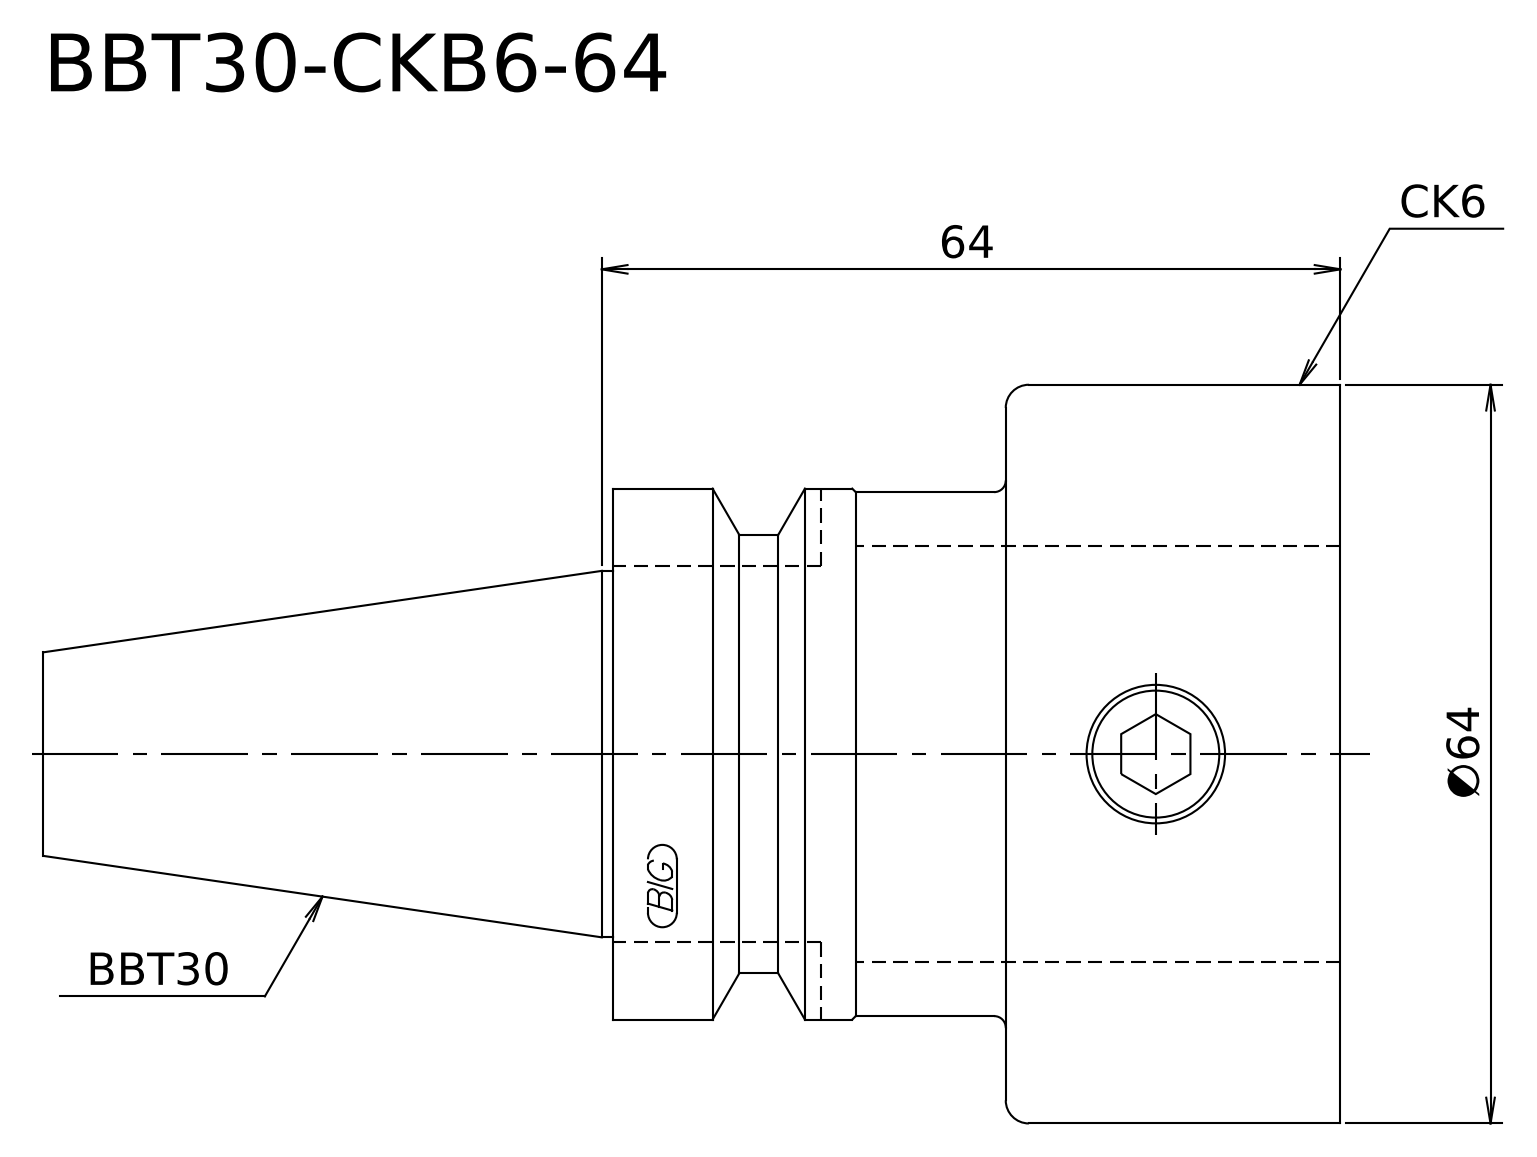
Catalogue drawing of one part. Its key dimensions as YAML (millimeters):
step_written_by: "Kubotek KeyCreator V8.5.1 (14335) (CONFIG_CONTROL_DESIGN)"
units: millimeters
bodies: {solids: 1, faces: 15, planar: 4, cylindrical: 6, other: 5}
overall_size: [112.4, 64, 64]
volume: 171094
surface_area: 20866
round_bosses_or_shafts:
  - {diameter: 64, count: 1}
  - {diameter: 46, count: 1}
  - {diameter: 45.4, count: 1}
  - {diameter: 38, count: 1}
  - {diameter: 31.75, count: 1}
face_to_face_distances: [29, 63, 34, 112.4, 83.4, 49.4]
